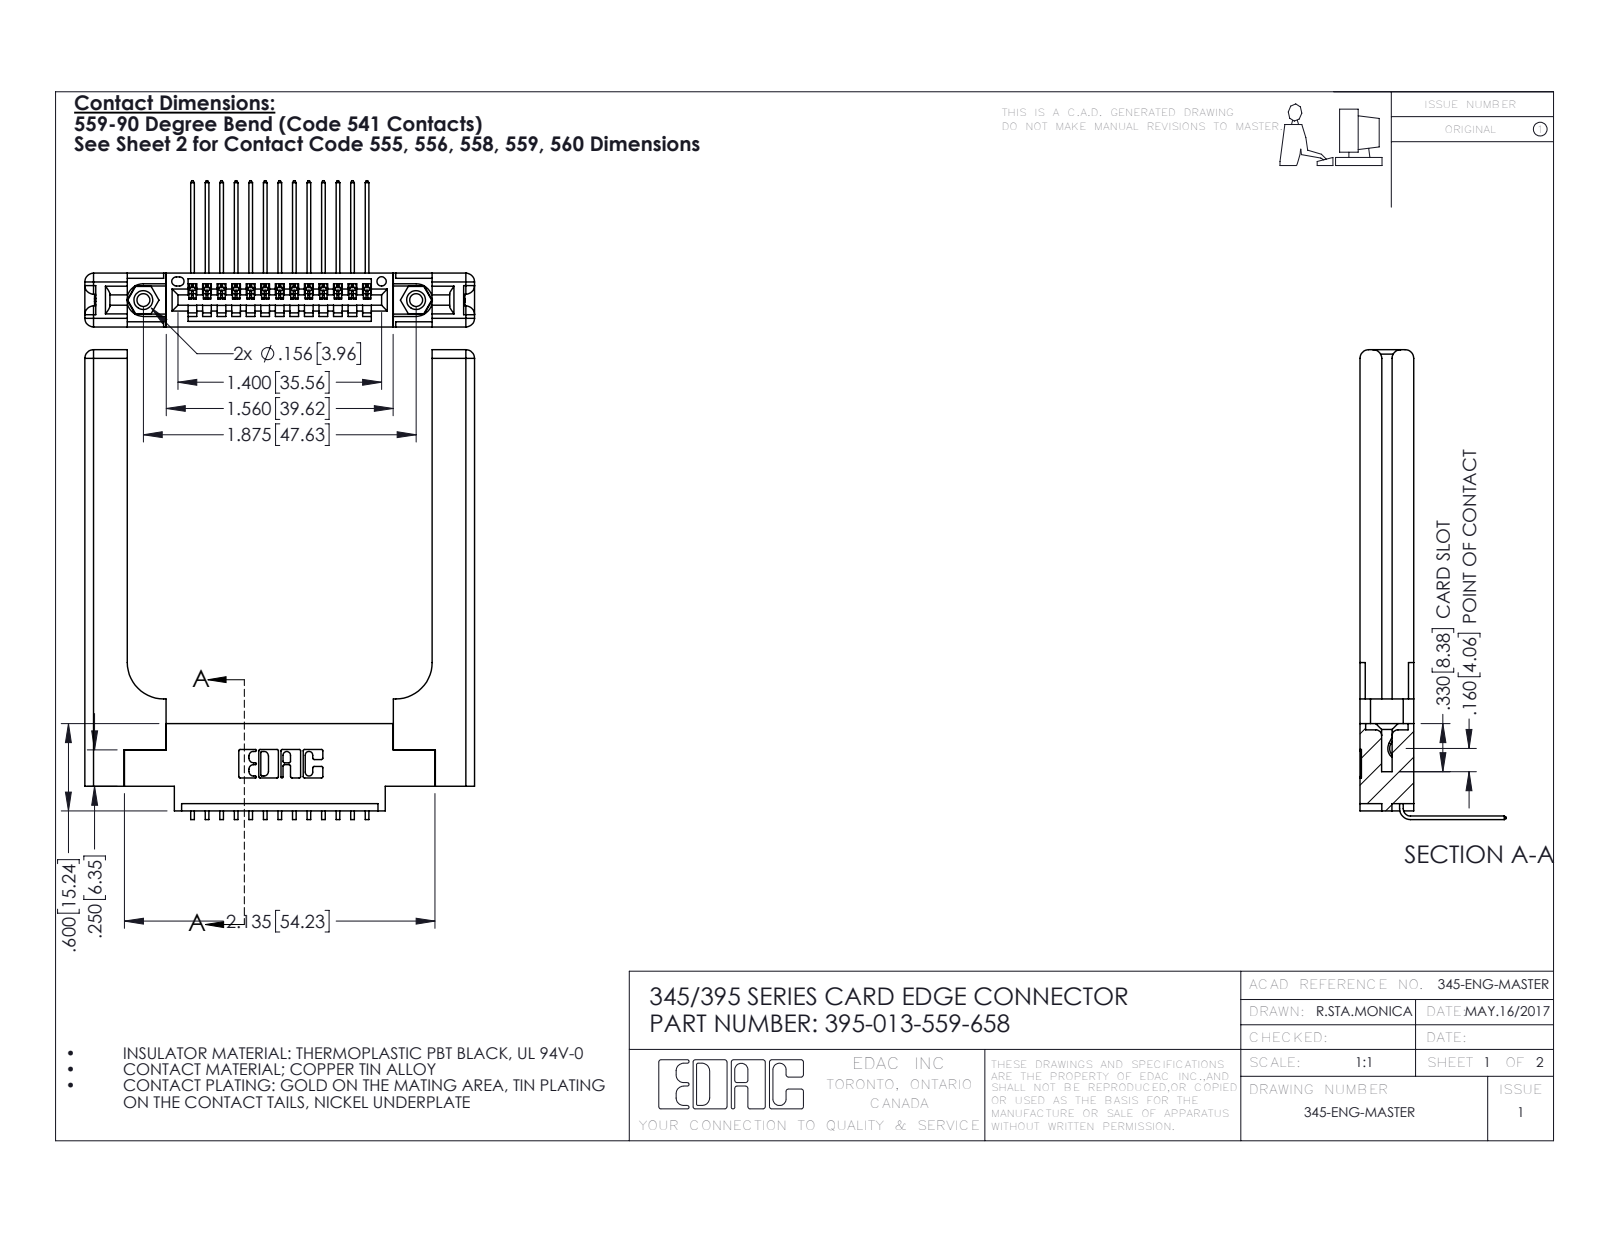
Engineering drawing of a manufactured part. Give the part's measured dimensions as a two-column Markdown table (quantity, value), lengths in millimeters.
| quantity | value |
| --- | --- |
| part name | 345-250-001_345-250-001-102; 345-220-058_345-220-058; 345-292-001_558 559 Tail - 1; 395-013-559-658 (+1 more) |
| STEP written by | SolidWorks 2016 (CONFIG_CONTROL_DESIGN) |
| units | millimeters |
| bodies | 18 solids, 1166 faces (778 planar, 328 cylindrical, 60 other) |
| overall size | 82 × 68 × 25.5 |
| volume | 14 700 mm³ |
| surface area | 13 470 mm² |
| round holes (diameter × count) | 2.3 × 2, 3.2 × 2, 4 × 2, 1.6 × 1 |
| round bosses / shafts (diameter × count) | 3.9 × 2 |
| partial cylindrical surfaces (radius × count) | 0.2 × 26, 0.3 × 22, 1.5 × 16, 0.2 × 6, 0.8 × 6, 0.7 × 3, 0.8 × 2, 0.8 × 2 |
| main face-to-face distances | 9.4, 1.8, 3.8, 3.8, 2, 5.6, 7.6, 3, 53.2, 1.8 |
| hole center spacings | 6.9, 41.7, 47.6 |
